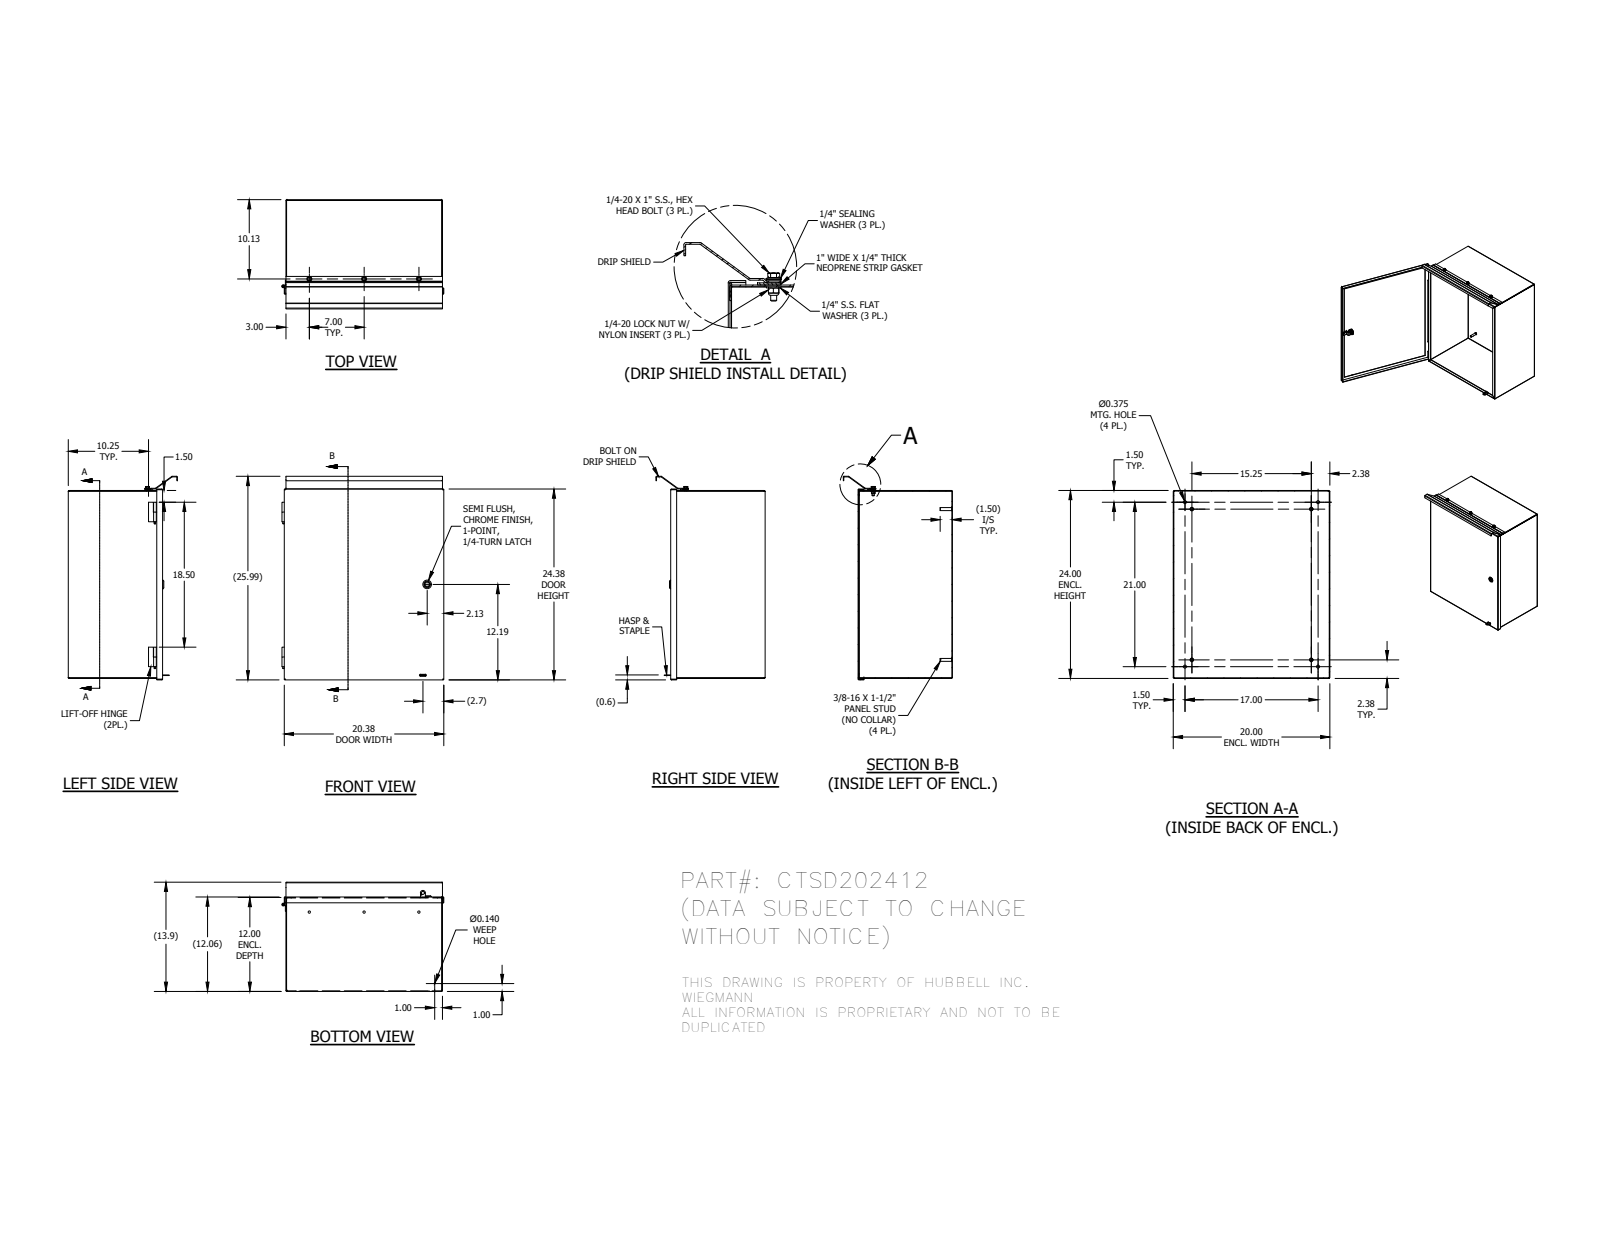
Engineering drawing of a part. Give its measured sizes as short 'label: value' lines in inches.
name: CTSD202412BKP; CTSD2024DR; 31815; HC2527 (+8 more)
written by: Autodesk Inventor 2014 (AUTOMOTIVE_DESIGN)
unit: in
bodies: 36 solids, 860 faces (456 planar, 259 cylindrical, 145 other)
size: 25.995 × 20.665 × 13.95
volume: 172.5 in³; area: 4 697 in²
holes: 5× ⌀0.375, 3× ⌀0.196, 3× ⌀0.235, 3× ⌀0.275, 3× ⌀0.281, 3× ⌀0.29, 1× ⌀0.125, 1× ⌀0.14, 1× ⌀0.197, 1× ⌀0.211, 1× ⌀0.219, 1× ⌀0.315
bosses: 4× ⌀0.462, 4× ⌀0.375, 3× ⌀0.65, 3× ⌀0.625, 3× ⌀0.6, 3× ⌀0.438, 3× ⌀0.435, 3× ⌀0.26
rounds: 30× R0.012, 20× R0.031, 18× R0.105, 10× R0.02, 8× R0.07, 4× R0.125, 4× R0.157, 3× R0.016
face distances: 0.074, 11.984, 19.926, 11.91, 12.058, 23.926, 20, 19.852, 23.852, 24
hole spacings: 7, 10.51, 17, 19.591, 21, 27.019, 0.288, 2.249
